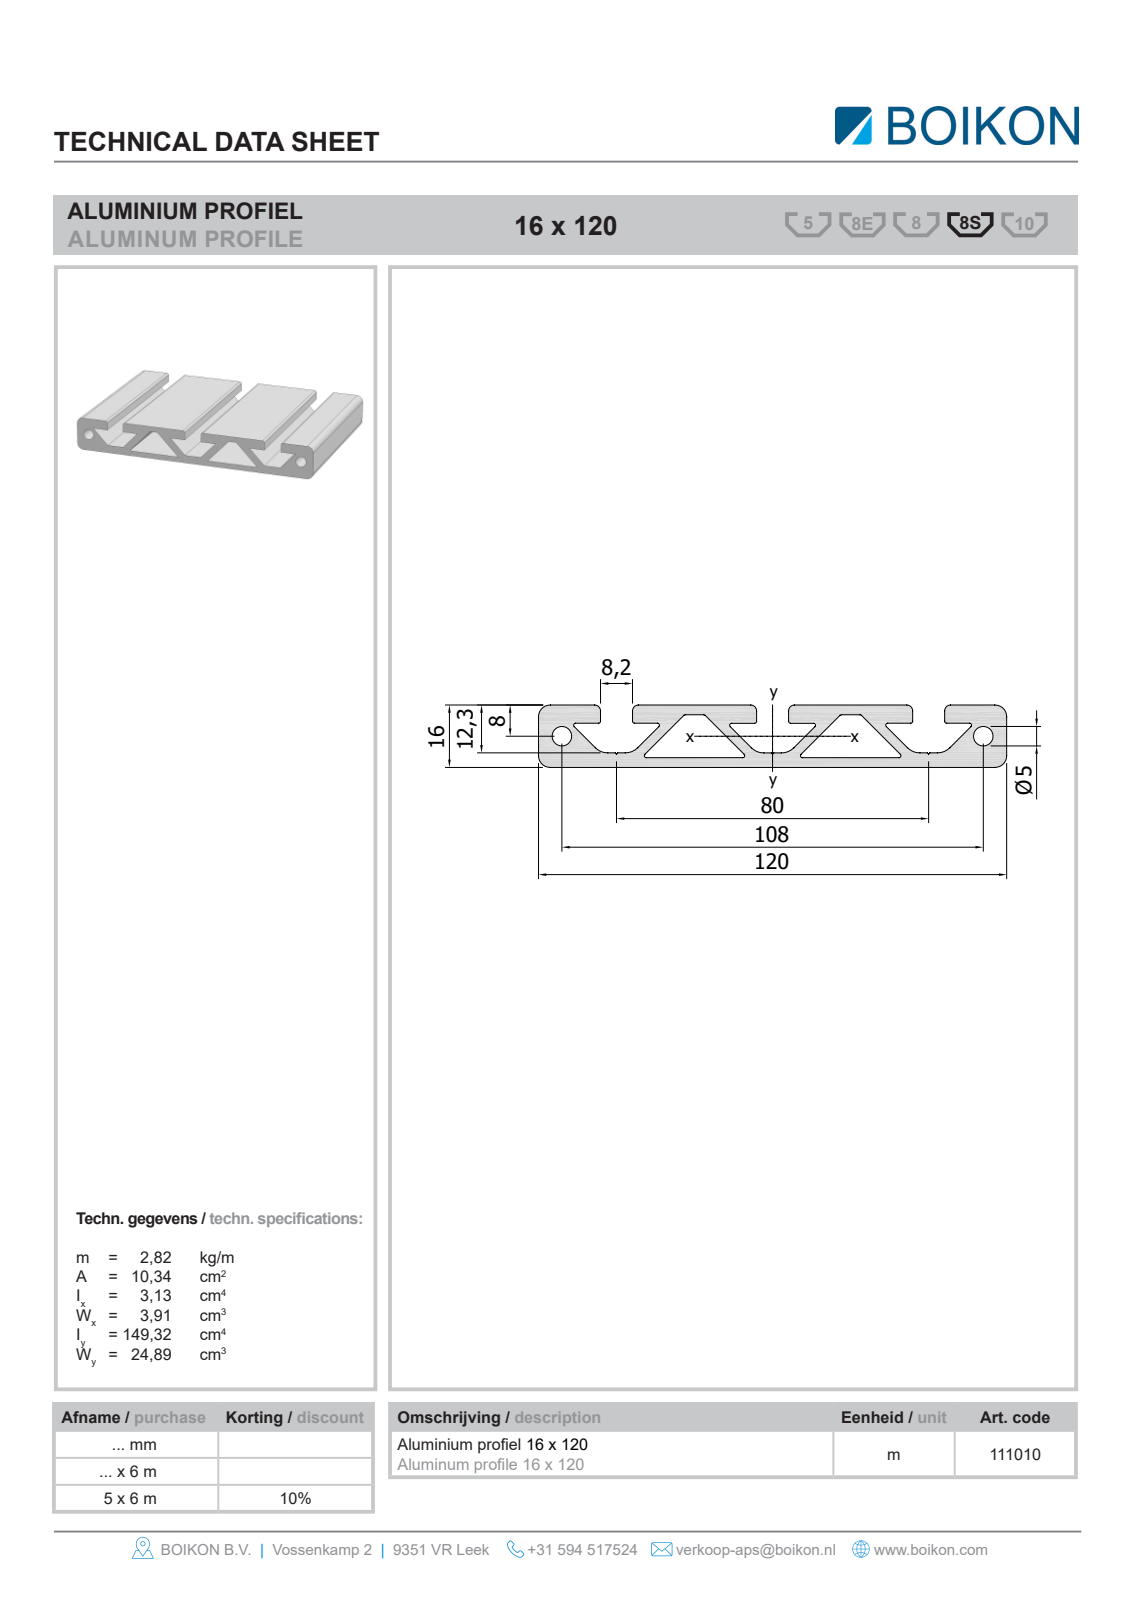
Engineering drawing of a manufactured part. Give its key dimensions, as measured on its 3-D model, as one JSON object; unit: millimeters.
{"part_name": "Root; 11101016x120BOIKON0", "step_written_by": "HiCAD 2013 1802.4 Build 509 (AUTOMOTIVE_DESIGN)", "units": "millimeters", "bodies": {"solids": 1, "faces": 50, "planar": 38, "cylindrical": 12, "other": 0}, "overall_size": [1000, 120, 16], "volume_mm3": 1085000, "surface_area_mm2": 552018, "round_holes": [[5, 2]], "partial_cylinders_radius": [[1, 6], [3, 4]], "face_to_face_distances": [16, 28.76, 2.5, 13.5, 11.5, 9, 4.5, 3.75, 1.25, 7.75], "hole_center_spacings": [108]}
